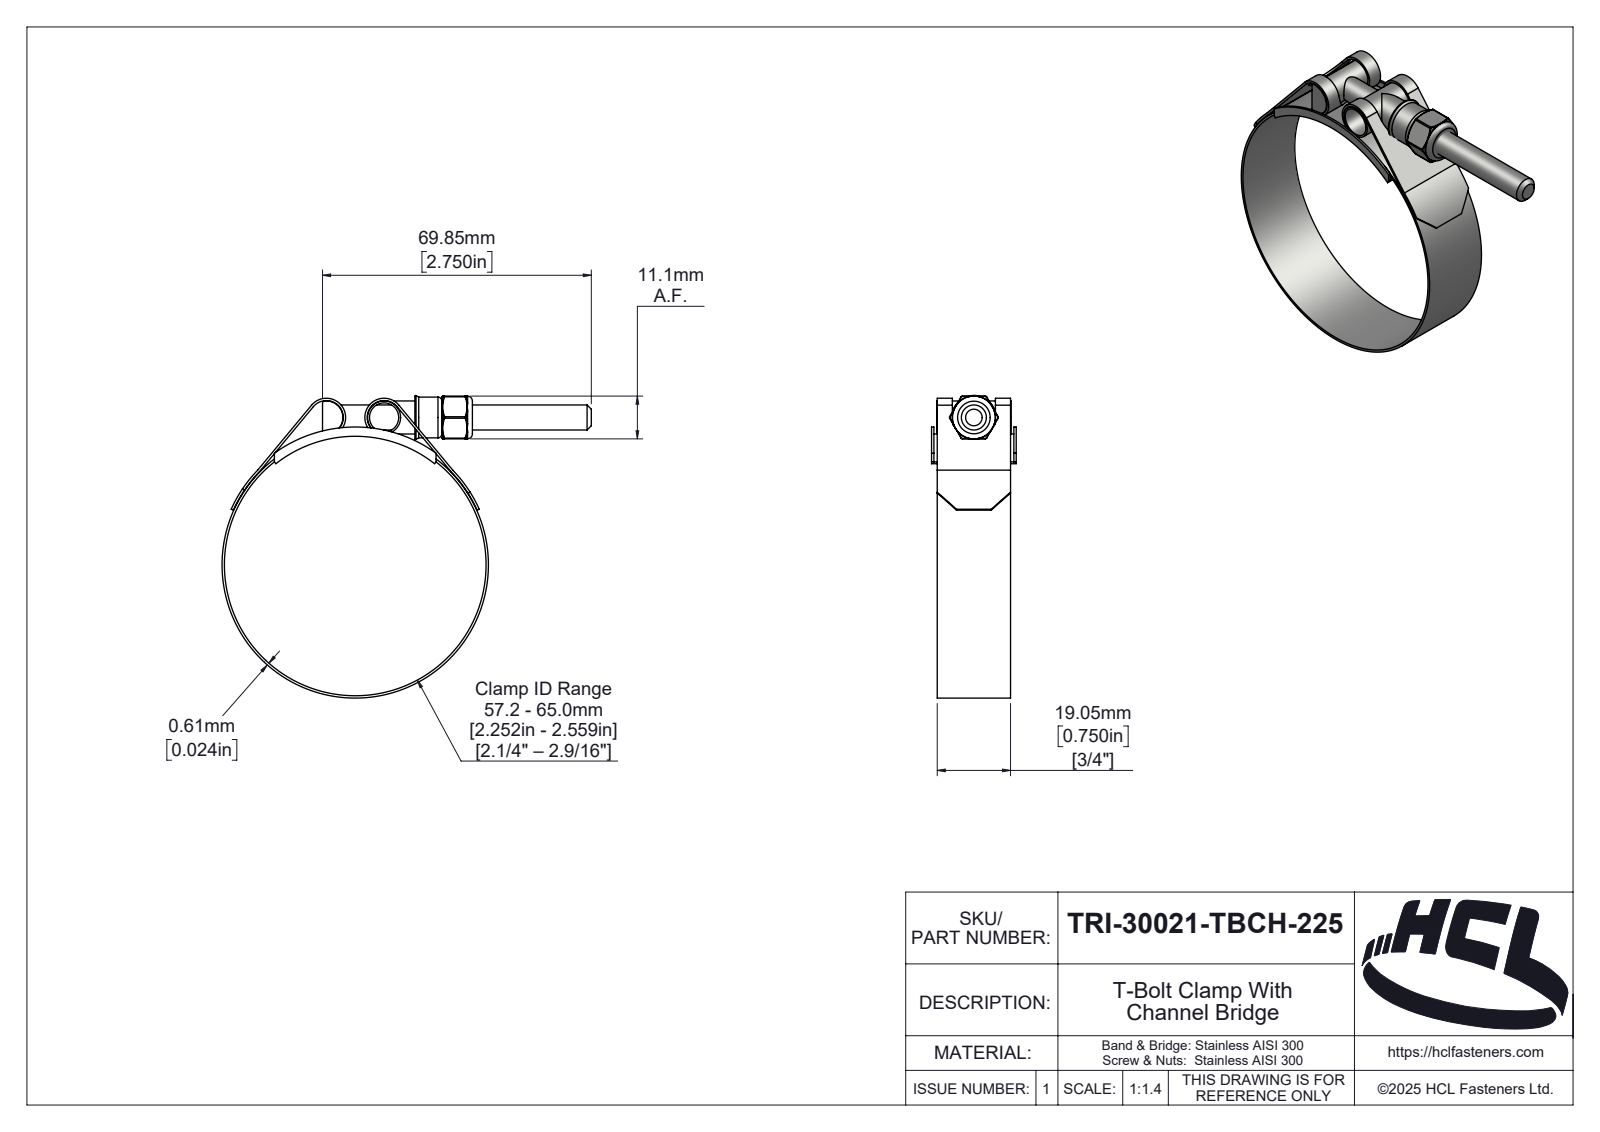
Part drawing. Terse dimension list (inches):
name: TRI-30021-TBCH-225
written by: SolidWorks 2025 (AUTOMOTIVE_DESIGN)
unit: in
bodies: 6 solids, 330 faces (46 planar, 122 cylindrical, 162 other)
size: 3.778 × 3.094 × 0.866
volume: 0.493 in³; area: 27.4 in²
holes: 1× ⌀0.213, 1× ⌀0.25, 1× ⌀0.256, 1× ⌀0.298, 1× ⌀2.677
bosses: 2× ⌀0.338, 1× ⌀2.725, 1× ⌀0.417
rounds: 6× R0.015, 2× R0.02, 2× R0.173, 2× R0.197, 1× R0.023, 1× R0.095, 1× R0.119, 1× R0.126
face distances: 0.024, 0.058, 0.808, 0.75, 0.842, 0.034, 0.784, 0.029, 0.866, 0.437
hole spacings: 1.535
